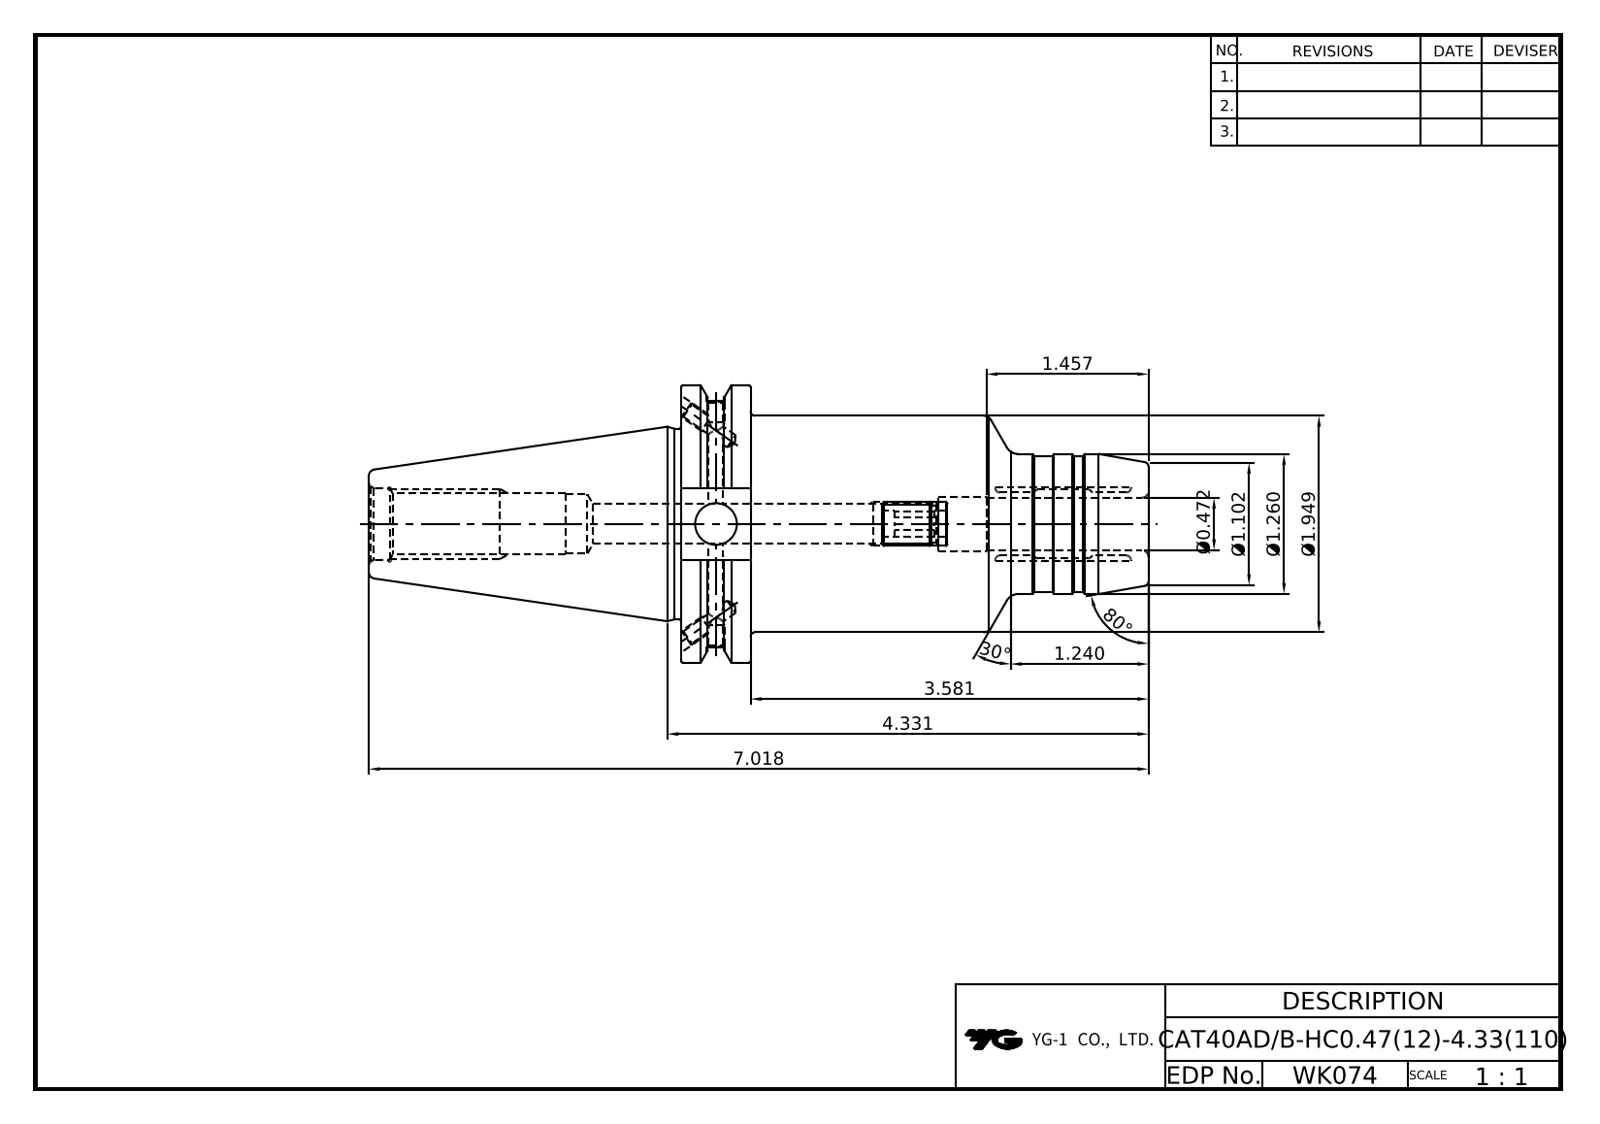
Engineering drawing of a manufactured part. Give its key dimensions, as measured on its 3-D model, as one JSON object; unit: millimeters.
{"part_name": "LO-CAT40ADB-HC12-110", "step_written_by": "Autodesk Inventor 2020 (AUTOMOTIVE_DESIGN)", "units": "millimeters", "bodies": {"solids": 1, "faces": 106, "planar": 34, "cylindrical": 35, "other": 37}, "overall_size": [178.25, 63.5, 61.09], "volume_mm3": 230245, "surface_area_mm2": 34926, "round_holes": [[3.24, 4], [4, 2], [4.2, 2], [8.92, 1], [9.53, 1], [12, 1], [12.6, 1], [13, 1], [13.39, 1], [16.3, 1]], "round_bosses_or_shafts": [[63.5, 1], [49.5, 1], [43.6, 1], [32, 1], [31, 1]], "partial_cylinders_radius": [[8.19, 1], [28.15, 1]], "face_to_face_distances": [15.88, 106.83, 90.95, 47.6, 16.38, 71.42, 87.3, 178.25, 77.47, 6.05]}
